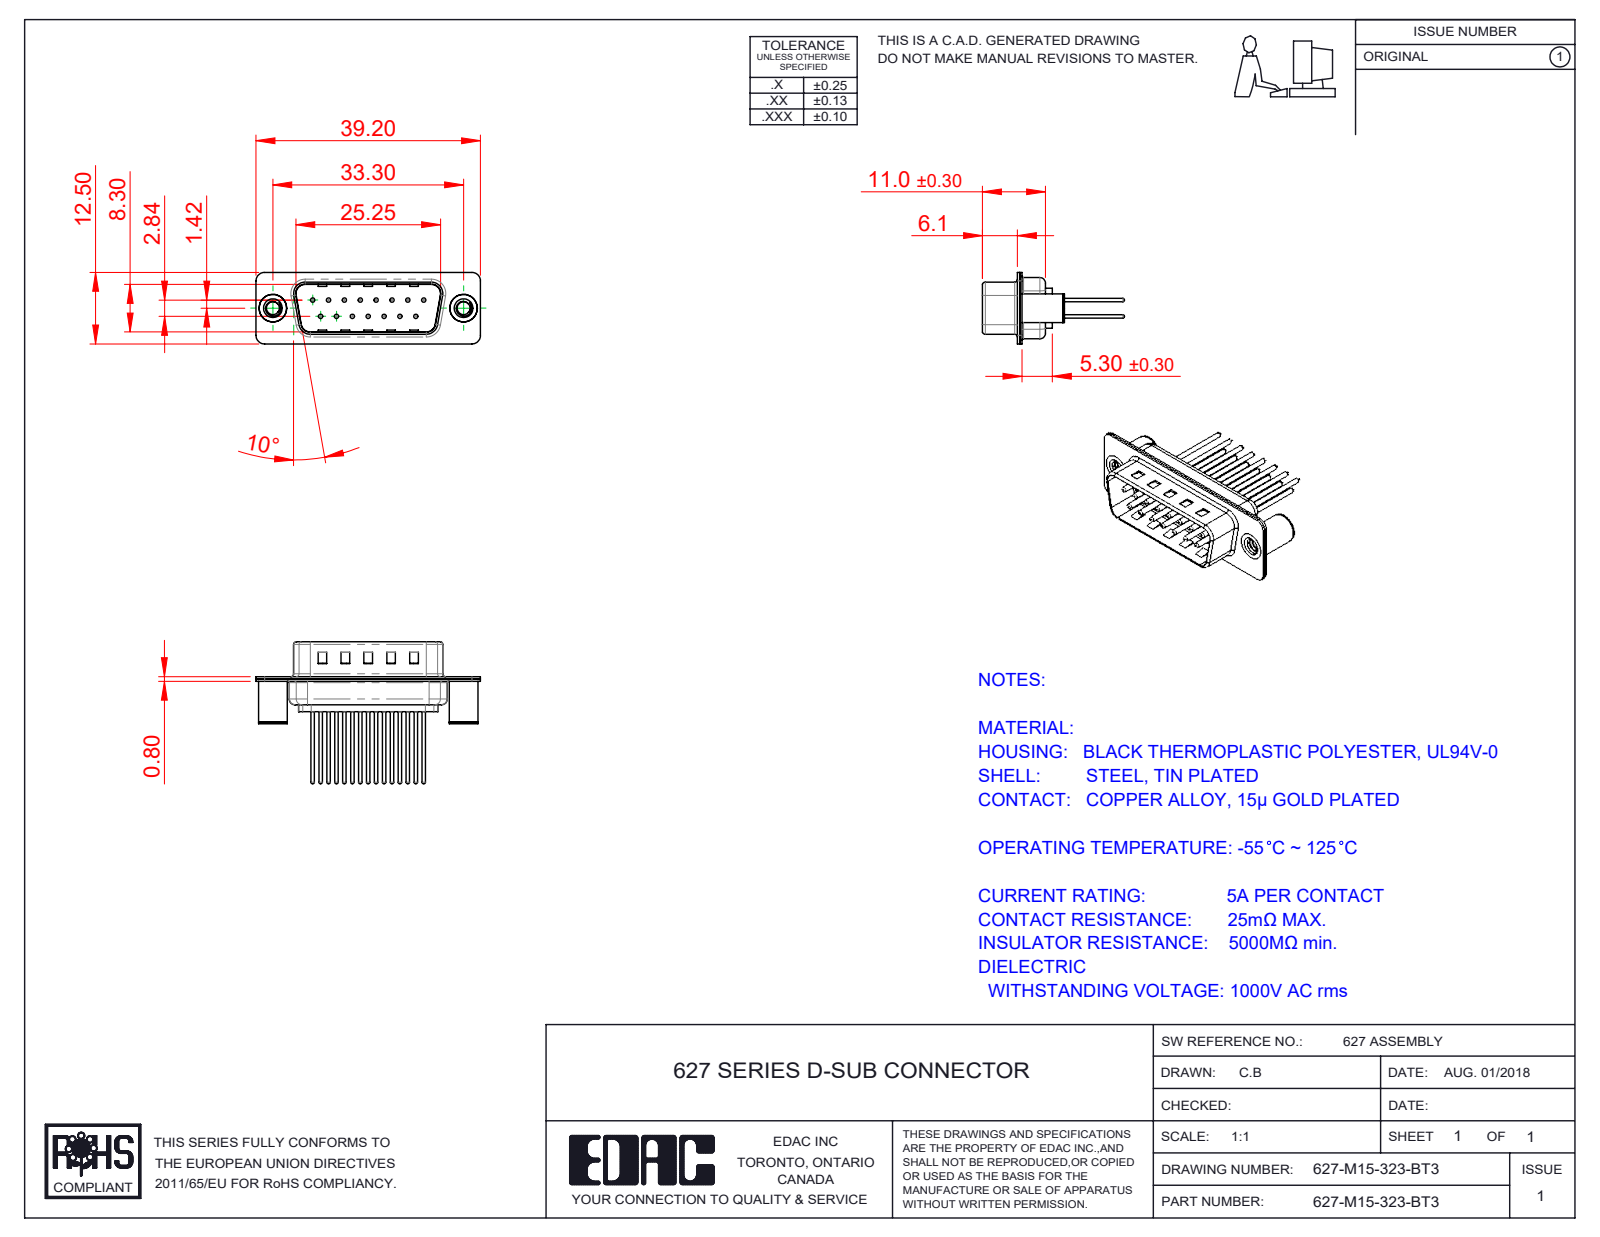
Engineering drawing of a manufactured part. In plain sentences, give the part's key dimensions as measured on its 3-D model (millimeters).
The part is named "627-M15-323-BT3; 627M Contact Row 2_23; 627M Shell Rear_15 Contacts; 627M Housing_15 Contacts (+3 more)". Its 3-D file was written by "SolidWorks 2020 (CONFIG_CONTROL_DESIGN)". It is 20 solids with 929 faces: 244 planar, 367 cylindrical and 318 other. Overall it measures 39.2 by 24.77 by 12.5 millimeters. Its volume is 1 995 cubic millimeters and its surface area 5 261 square millimeters. Round holes: 15 of diameter 0.75, 15 of diameter 1.6, 15 of diameter 2, 2 of diameter 2.26, 2 of diameter 3.26, 2 of diameter 4, 2 of diameter 4.8. Round bosses or shafts: 15 of diameter 1.5, 15 of diameter 0.6, 2 of diameter 5, 2 of diameter 4.9. Partial cylindrical surfaces (rounded edges, fillets, slot ends): 16 of radius 1.5, 12 of radius 2, 8 of radius 0.5, 8 of radius 1.6, 4 of radius 0.25, 4 of radius 0.6, 4 of radius 0.65, 4 of radius 0.9. The main face-to-face distances are 0.4, 0.8, 9.5, 9.1, 8.7, 9.9, 1.2, 5.3, 6.1, 5.7. The hole center spacings are 3.16, 2.77, 5.54, 8.31, 11.08, 5.03, 5.04, 7.48.
